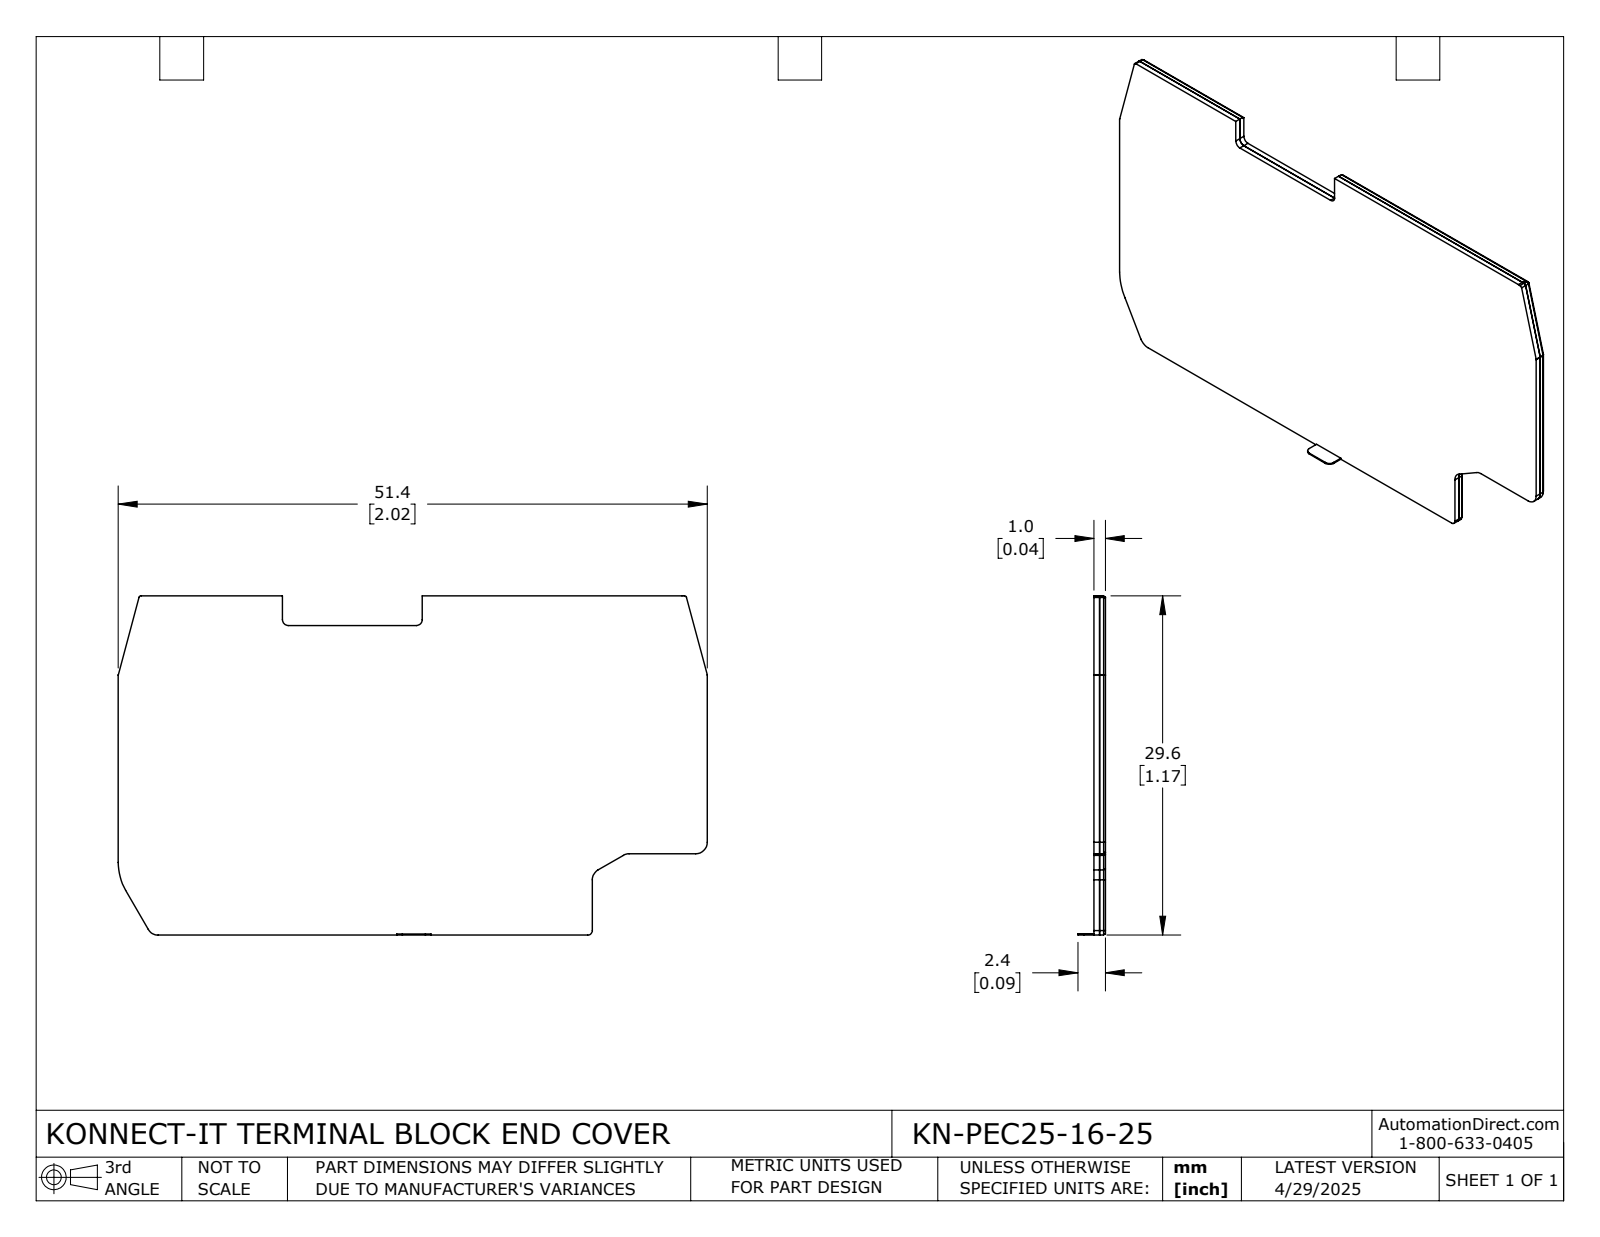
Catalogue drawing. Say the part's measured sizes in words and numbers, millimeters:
The part is named "KN-PEC25-16-25". Its 3-D file was written by "SolidWorks 2024 (CONFIG_CONTROL_DESIGN)". It is 2 solids with 86 faces: 50 planar, 36 cylindrical and 0 other. Overall it measures 51.43 by 29.61 by 2.4 millimeters. Its volume is 1 400 cubic millimeters and its surface area 5 776 square millimeters. Partial cylindrical surfaces (rounded edges, fillets, slot ends): 4 of radius 0.1, 4 of radius 0.2, 4 of radius 0.5, 4 of radius 1, 2 of radius 0.9, 2 of radius 1.1, 1 of radius 0.3, 1 of radius 0.4. The main face-to-face distances are 0.5, 1, 29.61, 29.51, 0.85, 0.35, 51.43, 27.02, 2.59, 26.92.
